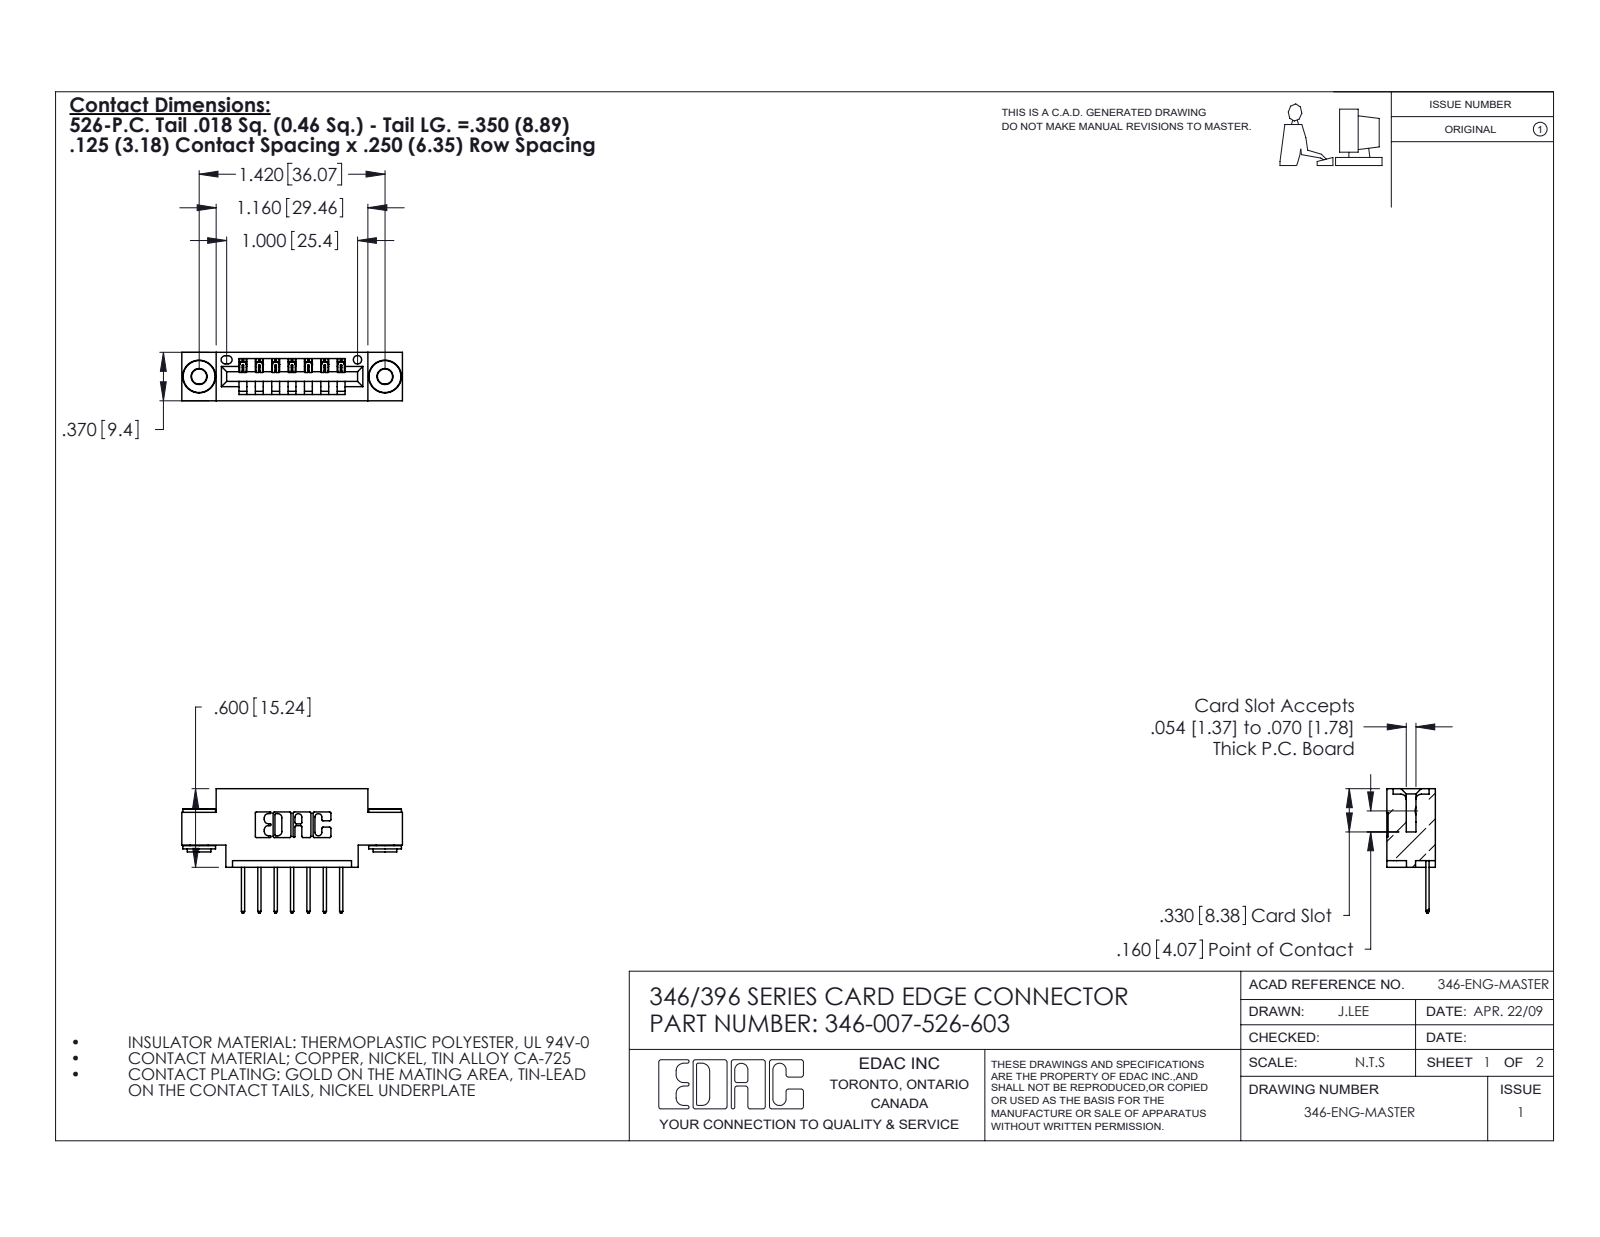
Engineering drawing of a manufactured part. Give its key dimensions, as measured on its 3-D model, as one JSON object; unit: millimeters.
{"part_name": "345-292-001_345-293-126; 346 Part_0.170 Offset - 0.156 Dia-TH; 346-007-526-603; 345-250-002_345-250-002-102", "step_written_by": "SolidWorks 2020 (CONFIG_CONTROL_DESIGN)", "units": "millimeters", "bodies": {"solids": 10, "faces": 584, "planar": 384, "cylindrical": 192, "other": 8}, "overall_size": [42.8, 24.1, 9.4], "volume_mm3": 3700, "surface_area_mm2": 4648, "round_holes": [[2.9, 2], [4, 2], [1.6, 1]], "round_bosses_or_shafts": [[6.4, 2], [4.6, 2], [3.5, 2]], "partial_cylinders_radius": [[0.3, 22], [0.2, 14], [0.3, 14], [0.2, 6], [0.8, 6], [0.7, 3], [0.8, 2], [1, 2]], "face_to_face_distances": [6.4, 9.4, 1.2, 8.2, 0.6, 5.6, 3.8, 2.5, 4.4, 1.8], "hole_center_spacings": [6.2, 30.9, 36.1]}
